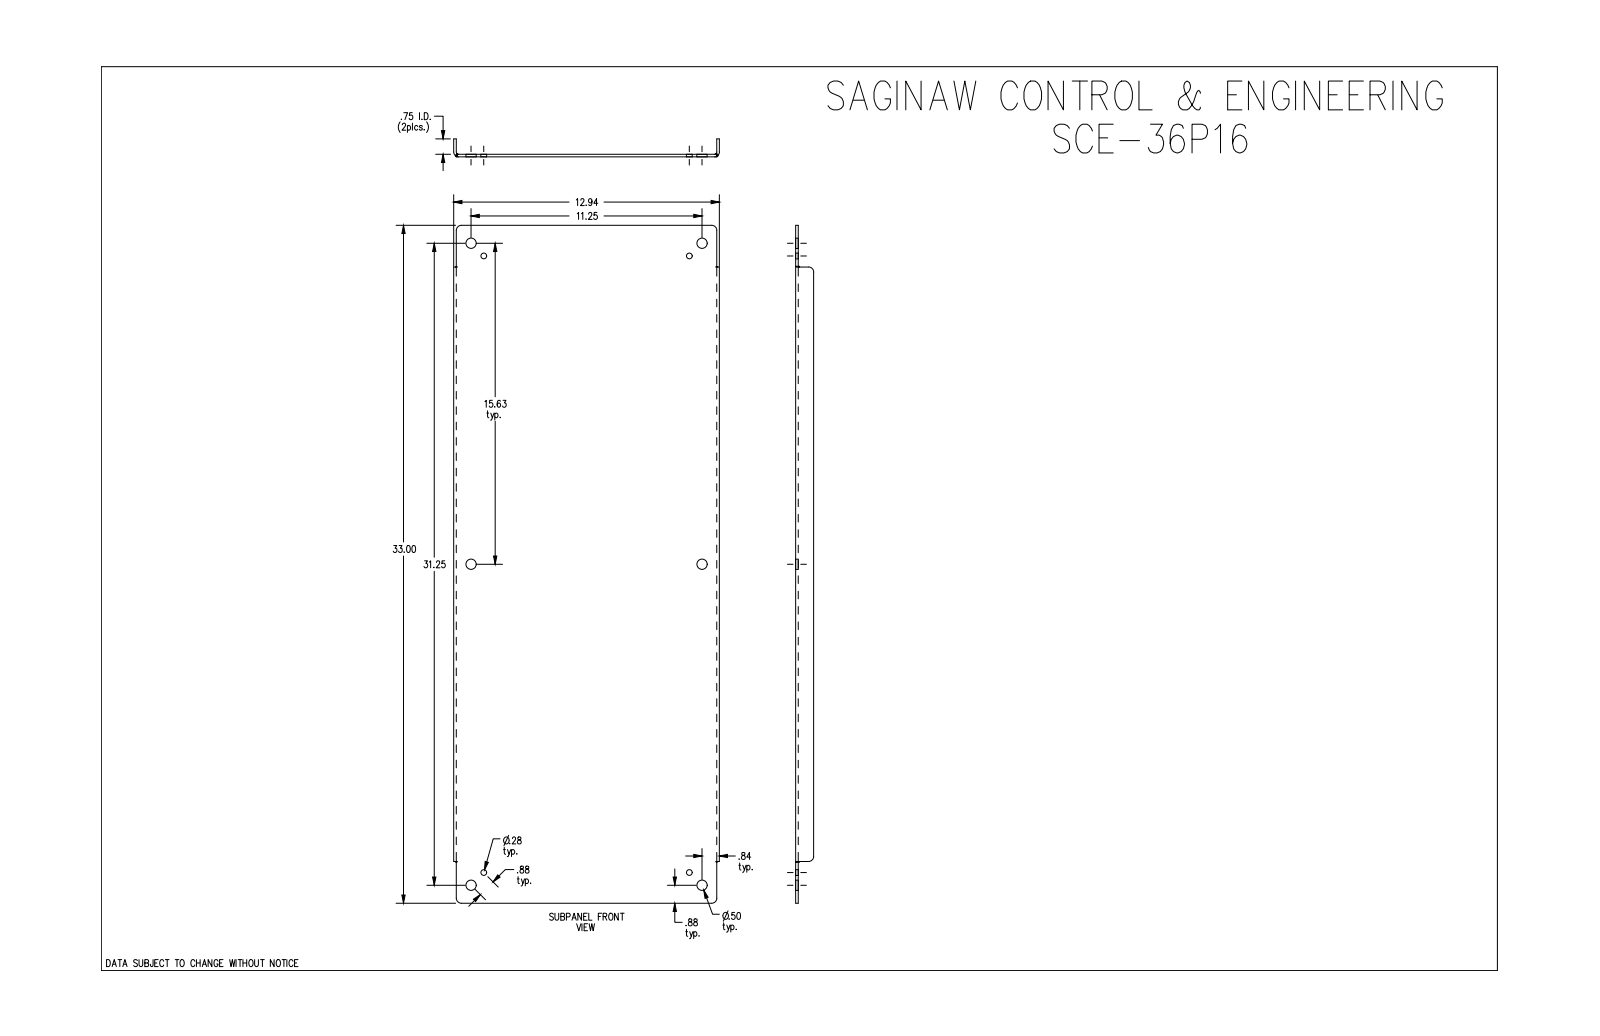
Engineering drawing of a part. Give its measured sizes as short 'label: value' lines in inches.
name: SCE-36P16
written by: SolidWorks 2019 (CONFIG_CONTROL_DESIGN)
unit: in
bodies: 1 solid, 52 faces (18 planar, 22 cylindrical, 12 other)
size: 33 × 12.938 × 0.875
volume: 57.93 in³; area: 940.3 in²
holes: 6× ⌀0.5, 4× ⌀0.281
rounds: 6× R0.25, 2× R0.112, 2× R0.237
face distances: 0.125, 0.125, 12.813, 12.687, 12.938, 0.75, 0.875, 33, 2.031, 30.969
hole spacings: 0.875, 10.65, 15.019, 15.625, 18.391, 19.254, 30.638, 32.424
